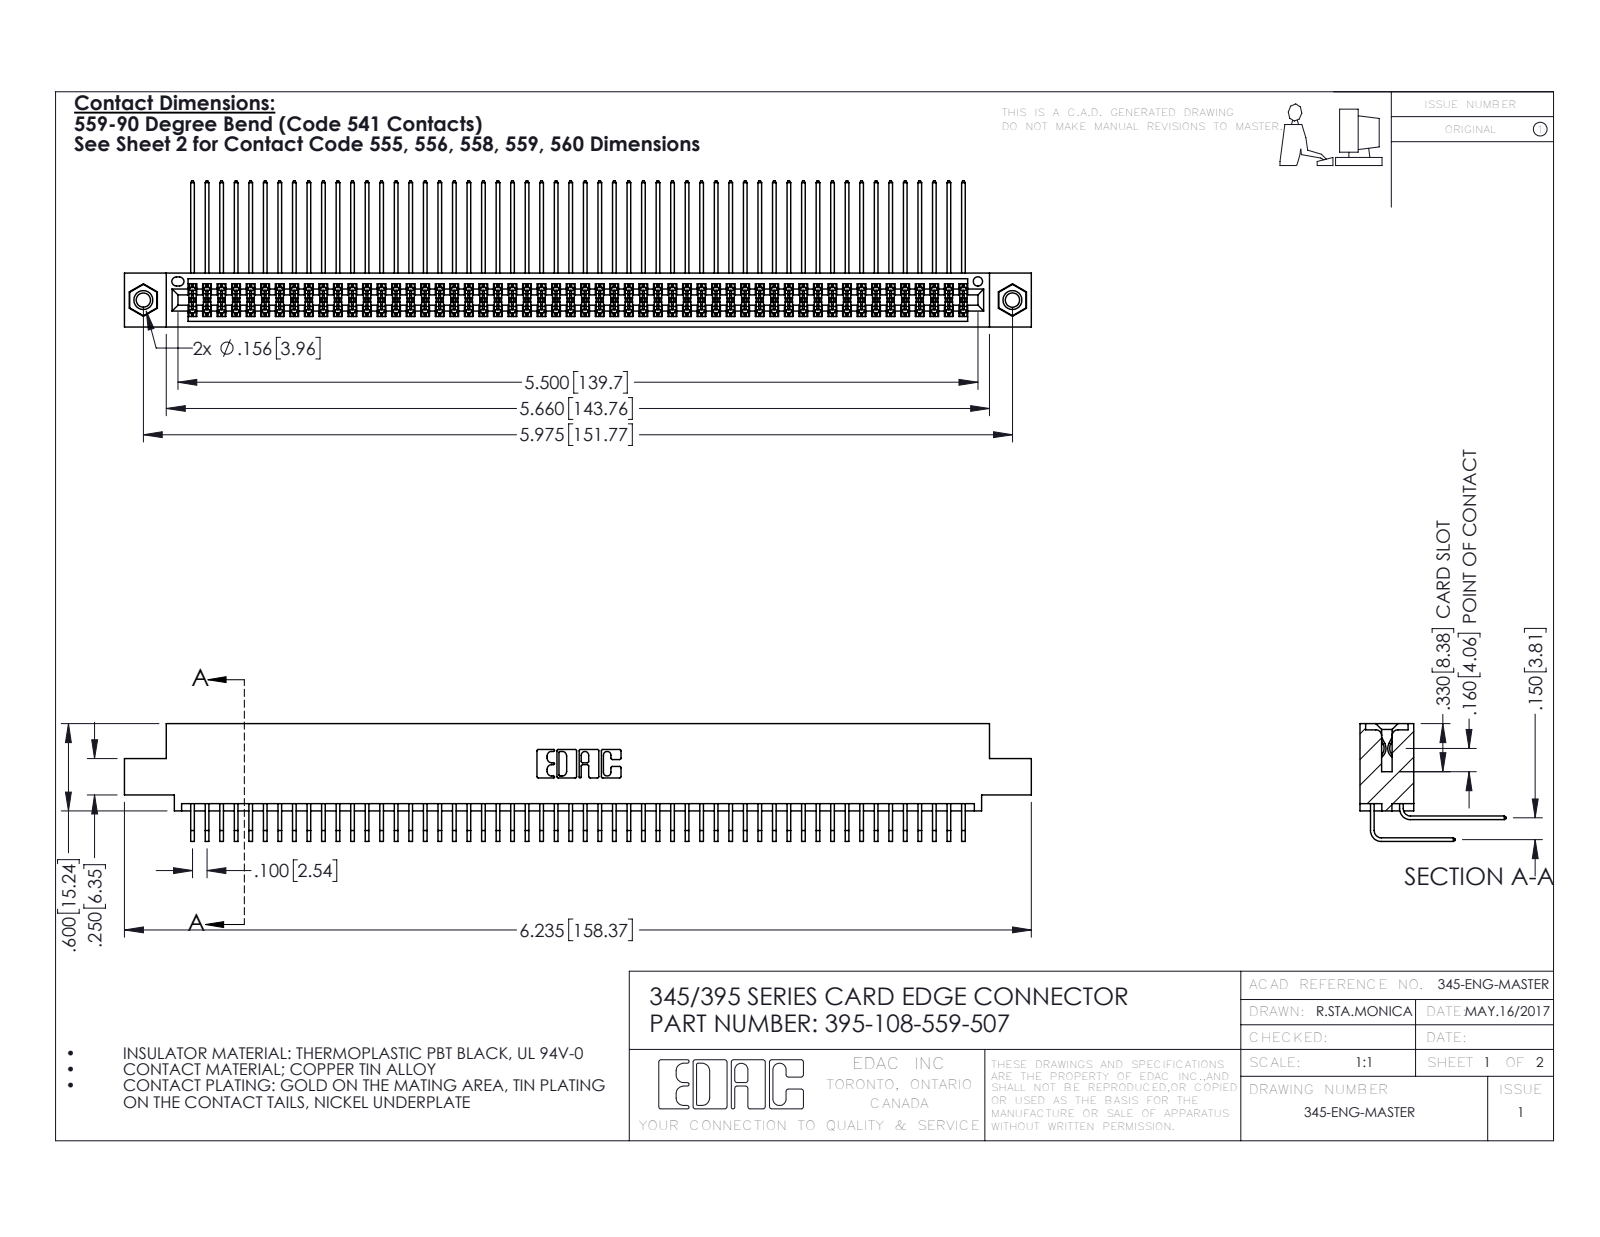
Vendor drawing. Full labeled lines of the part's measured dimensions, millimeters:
Part name (STEP PRODUCT): 345-292-001_558 559 Tail - 1; 345 Part_0.110 Offset - 0.156 Dia-TI; 345-250-001_345-250-005-103; 395-108-559-507 (+1 more)
STEP written by: SolidWorks 2016 (CONFIG_CONTROL_DESIGN)
Units: millimetres
Bodies: 111 solids, 5806 faces (3896 planar, 1894 cylindrical, 16 other)
Overall size (bounding box): 158.4 × 25.5 × 20.5
Volume: 16 000 mm³ · Surface area: 26 980 mm²
Round holes (diameter × count): ⌀2.5 ×2, ⌀3.2 ×2, ⌀4 ×2, ⌀1.6 ×1
Round bosses / shafts (diameter × count): ⌀3.9 ×2
Partial cylindrical surfaces — rounded edges, fillets, slot ends (radius × count): R0.2 ×163, R0.3 ×22, R0.2 ×6, R0.8 ×6, R0.7 ×3, R0.4 ×2, R0.5 ×2, R0.6 ×2
Main face-to-face distances: 1.8, 7.6, 5.1, 9.4, 2.5, 6.9, 0.6, 5.7, 4.4, 3.8
Hole centre spacings: 6.9, 145.8, 151.8
